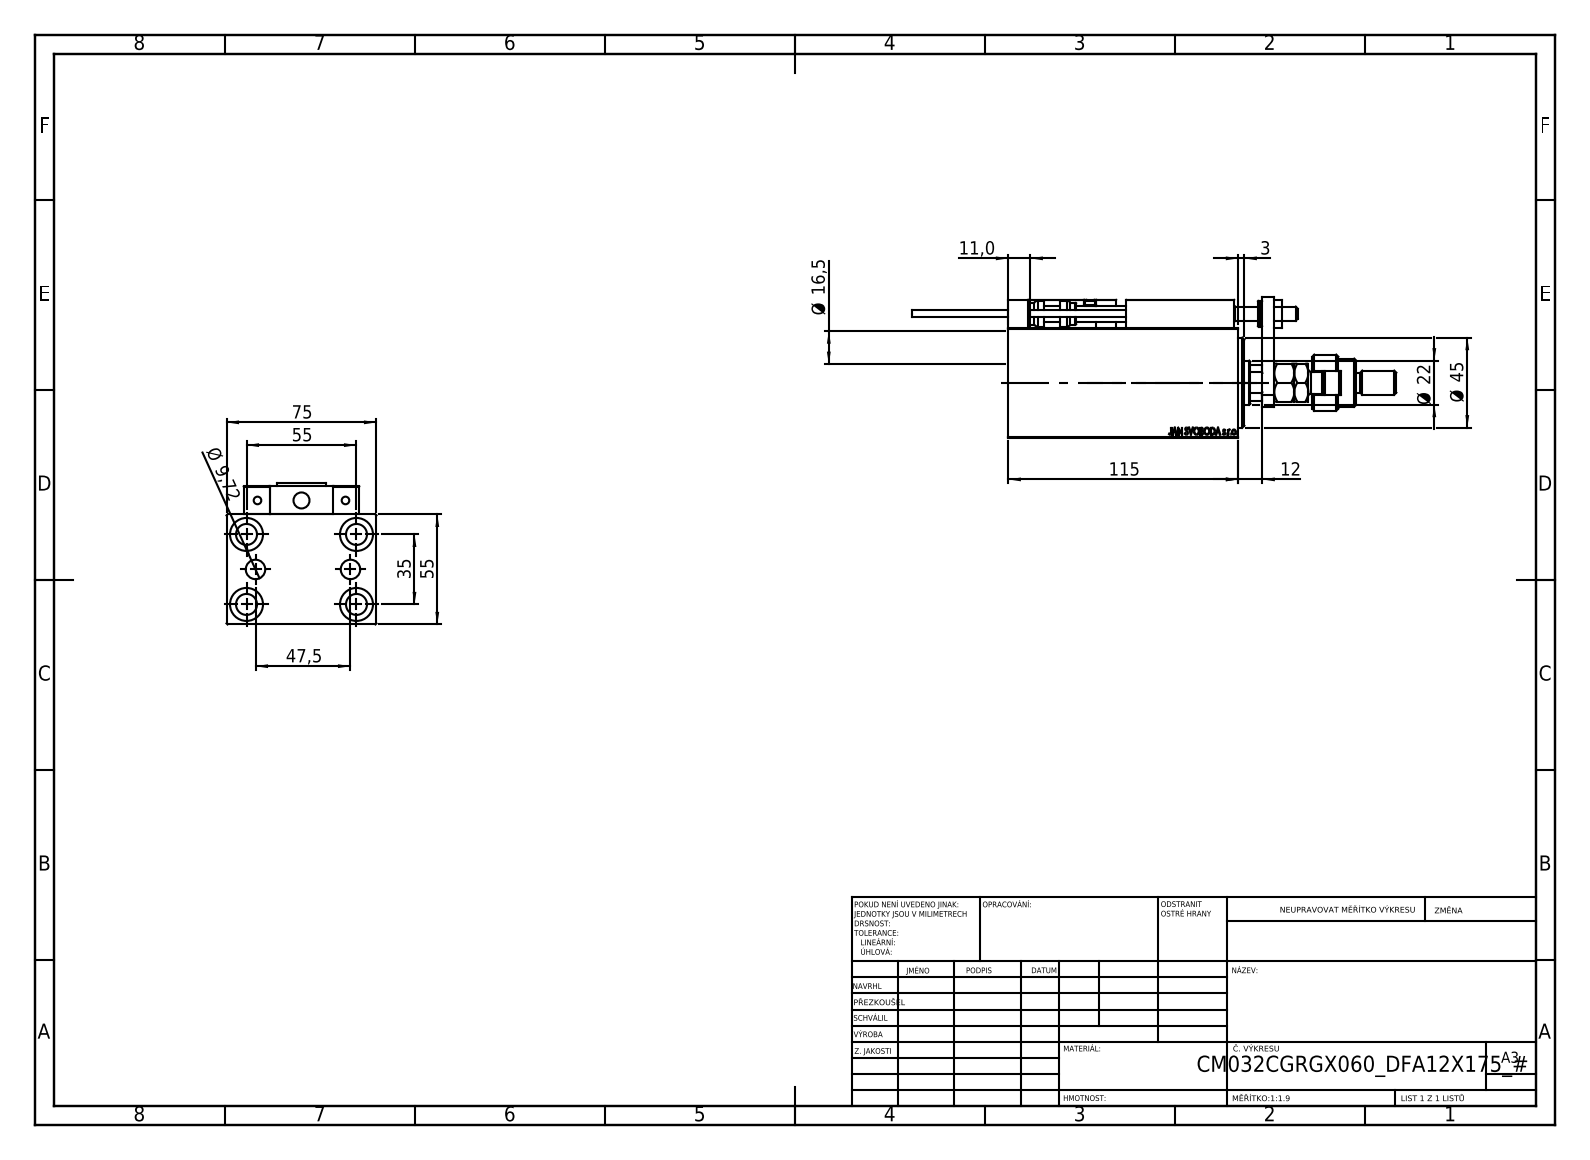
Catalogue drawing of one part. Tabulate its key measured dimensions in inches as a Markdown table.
| quantity | value |
| --- | --- |
| part name | V450CM_C_VCP; Block; SWITCH X; MAGNET (+8 more) |
| STEP written by | SolidWorks 2019 (CONFIG_CONTROL_DESIGN) |
| units | inches |
| bodies | 25 solids, 1357 faces (586 planar, 193 cylindrical, 578 other) |
| overall size | 9.528 × 2.953 × 2.776 |
| volume | 28.65 in³ |
| surface area | 177.3 in² |
| round holes (diameter × count) | 0.315 × 5, 0.413 × 5, 0.65 × 5, 0.126 × 4, 0.157 × 4, 0.197 × 2, 0.383 × 2, 0.276 × 1, 0.866 × 1, 1.004 × 1, 1.26 × 1, 1.339 × 1 |
| round bosses / shafts (diameter × count) | 0.433 × 2, 0.197 × 2, 0.15 × 2, 1.102 × 1, 0.945 × 1, 0.709 × 1, 0.512 × 1, 0.472 × 1 |
| partial cylindrical surfaces (radius × count) | 0.012 × 30, 0.118 × 2, 0.384 × 1, 0.413 × 1 |
| main face-to-face distances | 2.165, 2.953, 0.551, 0.394, 0.472, 0.709, 0.984, 0.276, 0.236, 2.717 |
| hole center spacings | 1.283, 0.448, 0.699, 0.711, 0.787, 1.165, 1.169, 1.273 |
